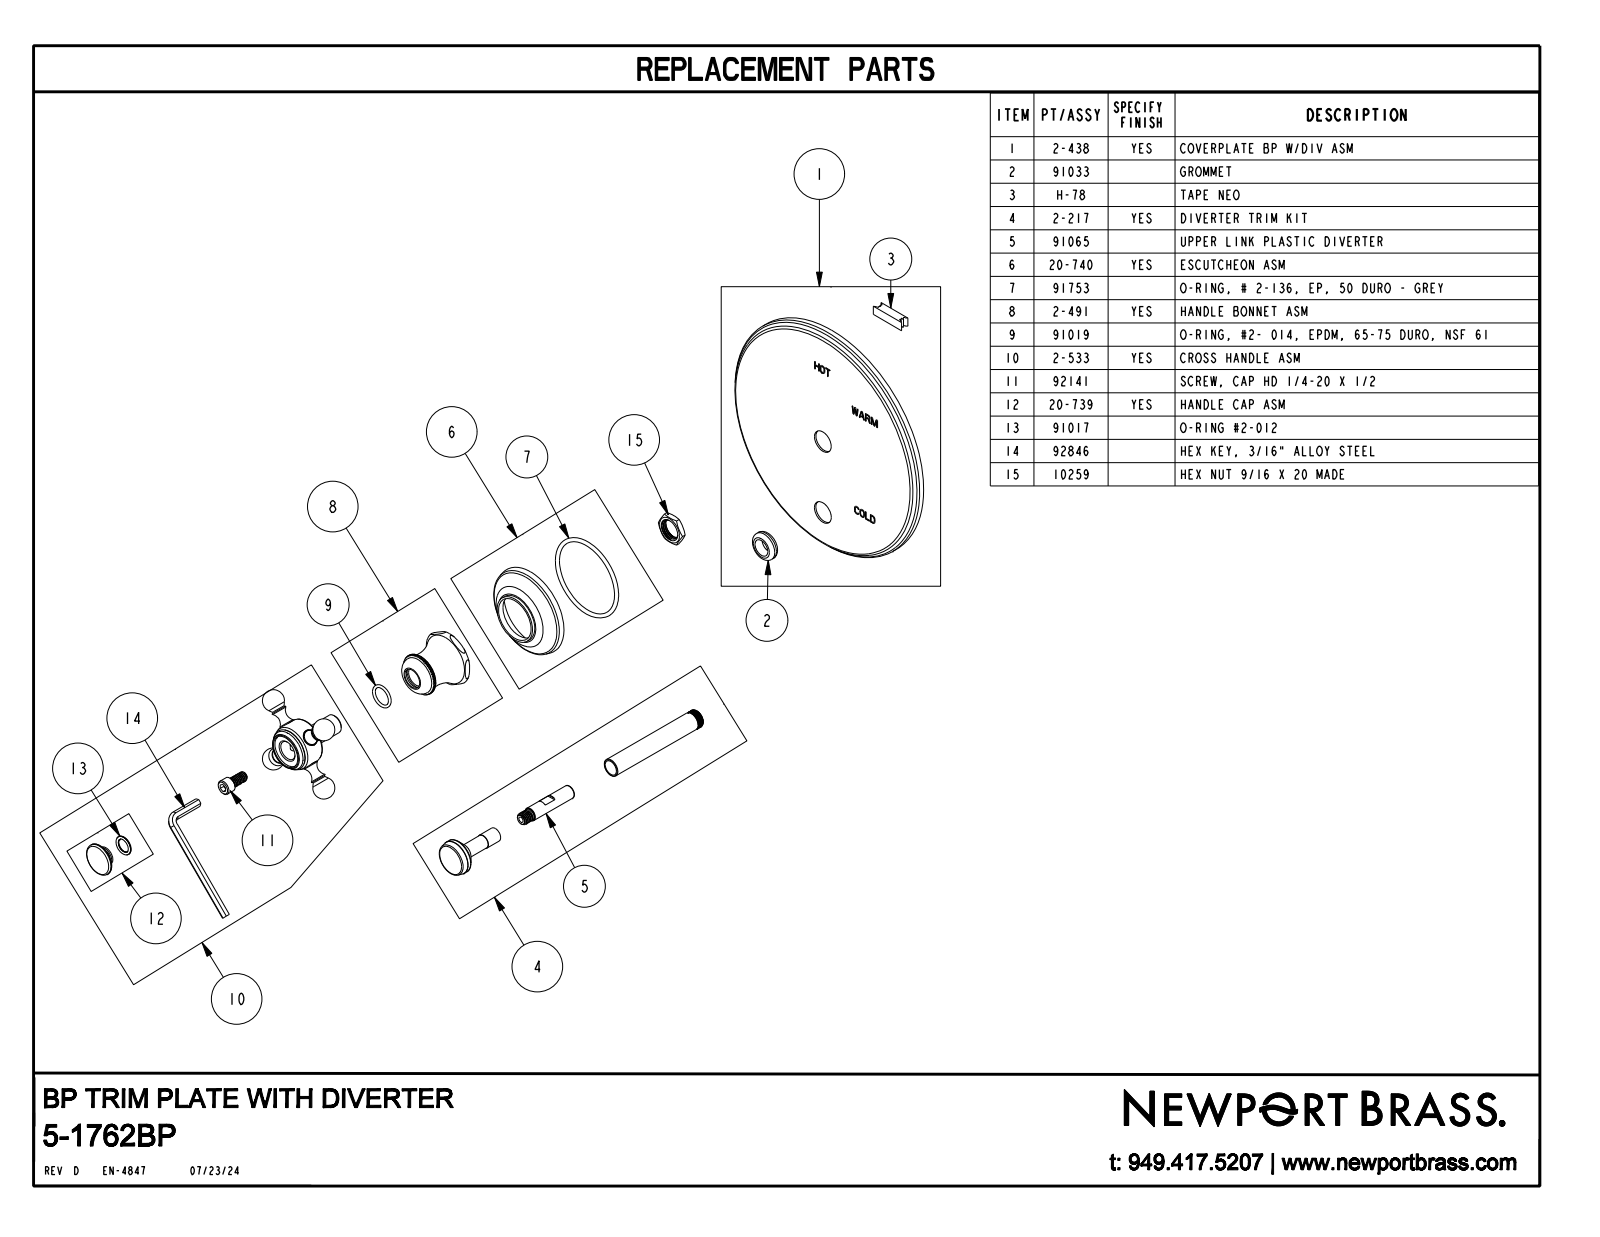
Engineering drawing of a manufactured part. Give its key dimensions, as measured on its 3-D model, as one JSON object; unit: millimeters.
{"part_name": "5-1762BP", "step_written_by": "CREO PARAMETRIC BY PTC INC, 2018400 (CONFIG_CONTROL_DESIGN)", "units": "millimeters", "bodies": {"solids": 1, "faces": 560, "planar": 424, "cylindrical": 30, "other": 106}, "overall_size": [165.1, 165.1, 94.6], "volume_mm3": 240100, "surface_area_mm2": 58510, "round_holes": [[10.4, 2], [21.7, 1]], "round_bosses_or_shafts": [[10, 2], [165.1, 1], [22.9, 1], [21.3, 1], [12.7, 1], [12, 1], [9, 1]], "face_to_face_distances": [8, 42.3, 34.3, 72.5, 64.5, 30.2, 34.9, 7.8, 34.4, 64.6]}
